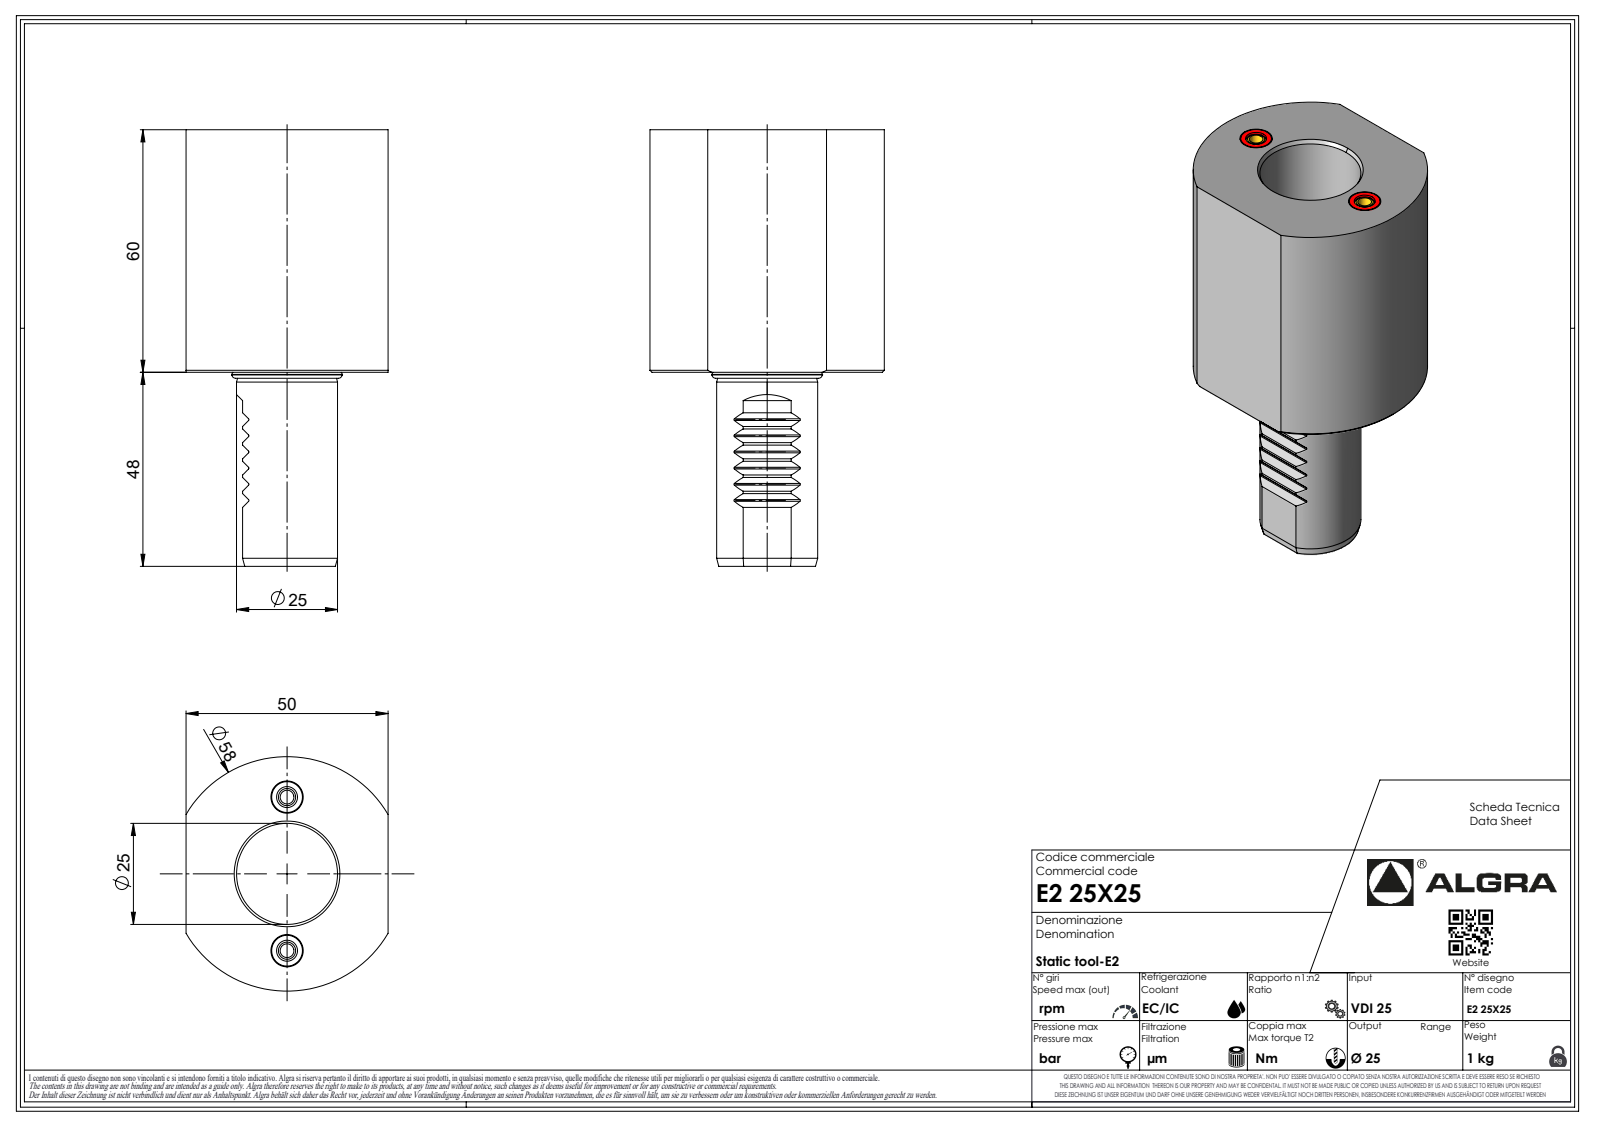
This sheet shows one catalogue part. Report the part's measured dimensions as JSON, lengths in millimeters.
{"part_name": "E2 25X25", "step_written_by": "SolidWorks 2023 (AUTOMOTIVE_DESIGN)", "units": "millimeters", "bodies": {"solids": 2, "faces": 258, "planar": 177, "cylindrical": 37, "other": 44}, "overall_size": [108, 58, 50], "volume_mm3": 146521, "surface_area_mm2": 24737, "round_holes": [[1.57, 1], [25, 1]], "round_bosses_or_shafts": [[27.47, 1], [4.77, 1], [1.28, 1]], "partial_cylinders_radius": [[0.25, 7], [0.39, 7], [2.78, 7], [0.3, 6], [0.16, 1], [29, 1]], "face_to_face_distances": [60, 50, 0.5, 60.5, 9, 51, 9.5, 108, 57, 48]}
